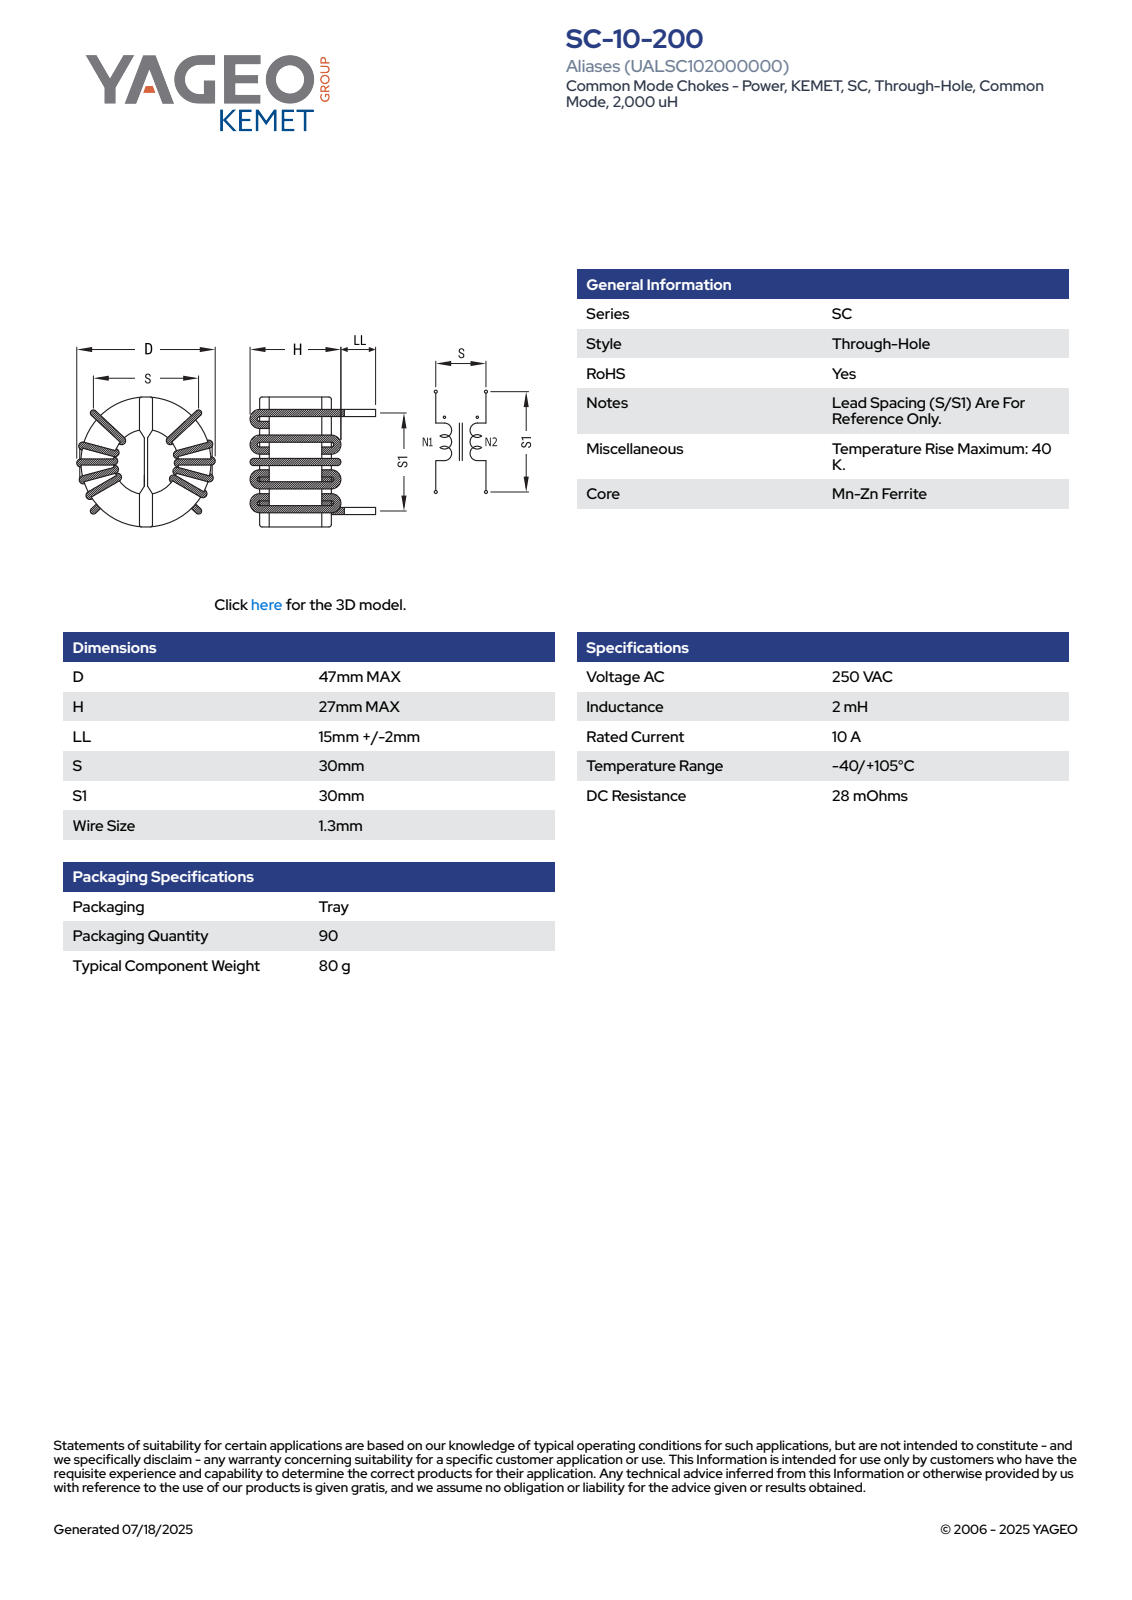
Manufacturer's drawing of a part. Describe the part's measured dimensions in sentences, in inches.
The part is named "SC-10-200". Its 3-D file was written by "SolidWorks 2018 (AUTOMOTIVE_DESIGN)". It is 1 solid with 397 faces: 139 planar, 131 cylindrical and 127 other. Overall it measures 1.85 by 1.685 by 1.654 inches. Its volume is 2.052 cubic inches and its surface area 18.13 square inches. Round holes: 1 of diameter 0.52. Round bosses or shafts: 10 of diameter 0.051. Partial cylindrical surfaces (rounded edges, fillets, slot ends): 36 of radius 0.035, 10 of radius 0.008, 2 of radius 0.02, 2 of radius 0.026, 2 of radius 0.043, 1 of radius 0.341, 1 of radius 0.368, 1 of radius 0.372. The main face-to-face distances are 0.933, 0.047, 0.079, 0.031, 0.224, 0.504, 0.126, 0.157, 0.776, 0.22.
